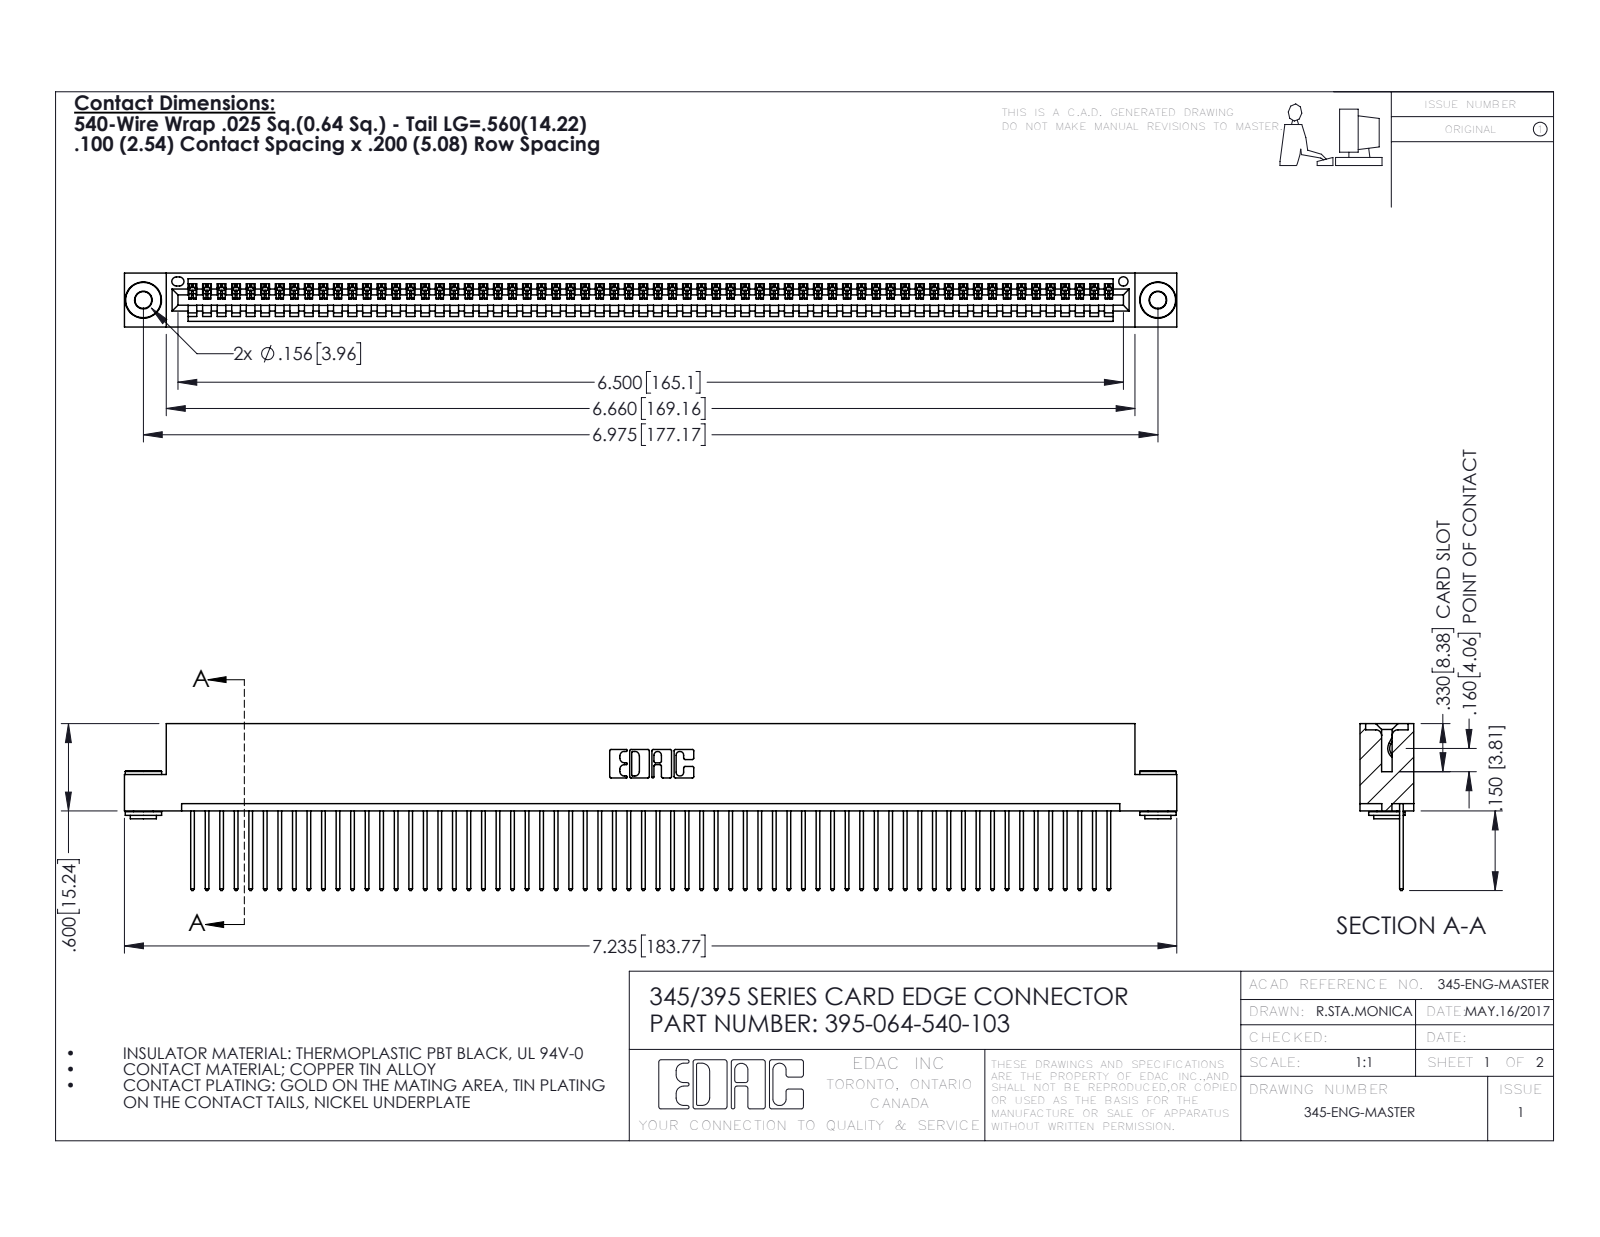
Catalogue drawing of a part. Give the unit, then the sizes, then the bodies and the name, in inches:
Units: inches
Overall size (bounding box): 7.235 × 1.147 × 0.37
Round holes (diameter × count): ⌀0.116 ×2, ⌀0.156 ×2, ⌀0.064 ×1
Round bosses / shafts (diameter × count): ⌀0.25 ×2, ⌀0.18 ×2, ⌀0.136 ×2
Partial cylindrical surfaces — rounded edges, fillets, slot ends (radius × count): R0.006 ×128, R0.01 ×128, R0.01 ×22, R0.007 ×6, R0.031 ×6, R0.026 ×3, R0.031 ×2, R0.04 ×2
Main face-to-face distances: 0.072, 0.298, 0.025, 0.37, 0.098, 0.272, 0.2, 0.225, 0.149, 0.072
Hole centre spacings: 0.27, 6.739, 6.975
Volume: 1.083 in³ · Surface area: 38.31 in²
Bodies: 67 solids, 3876 faces (2650 planar, 1218 cylindrical, 8 other)
Part name (STEP PRODUCT): 345 Part_Flush Mounting Lugs - 0.156 Dia-TH; 395-064-540-103; 345-292-001_345-293-140; 345-250-002_345-250-002-102
STEP written by: SolidWorks 2016 (CONFIG_CONTROL_DESIGN)
